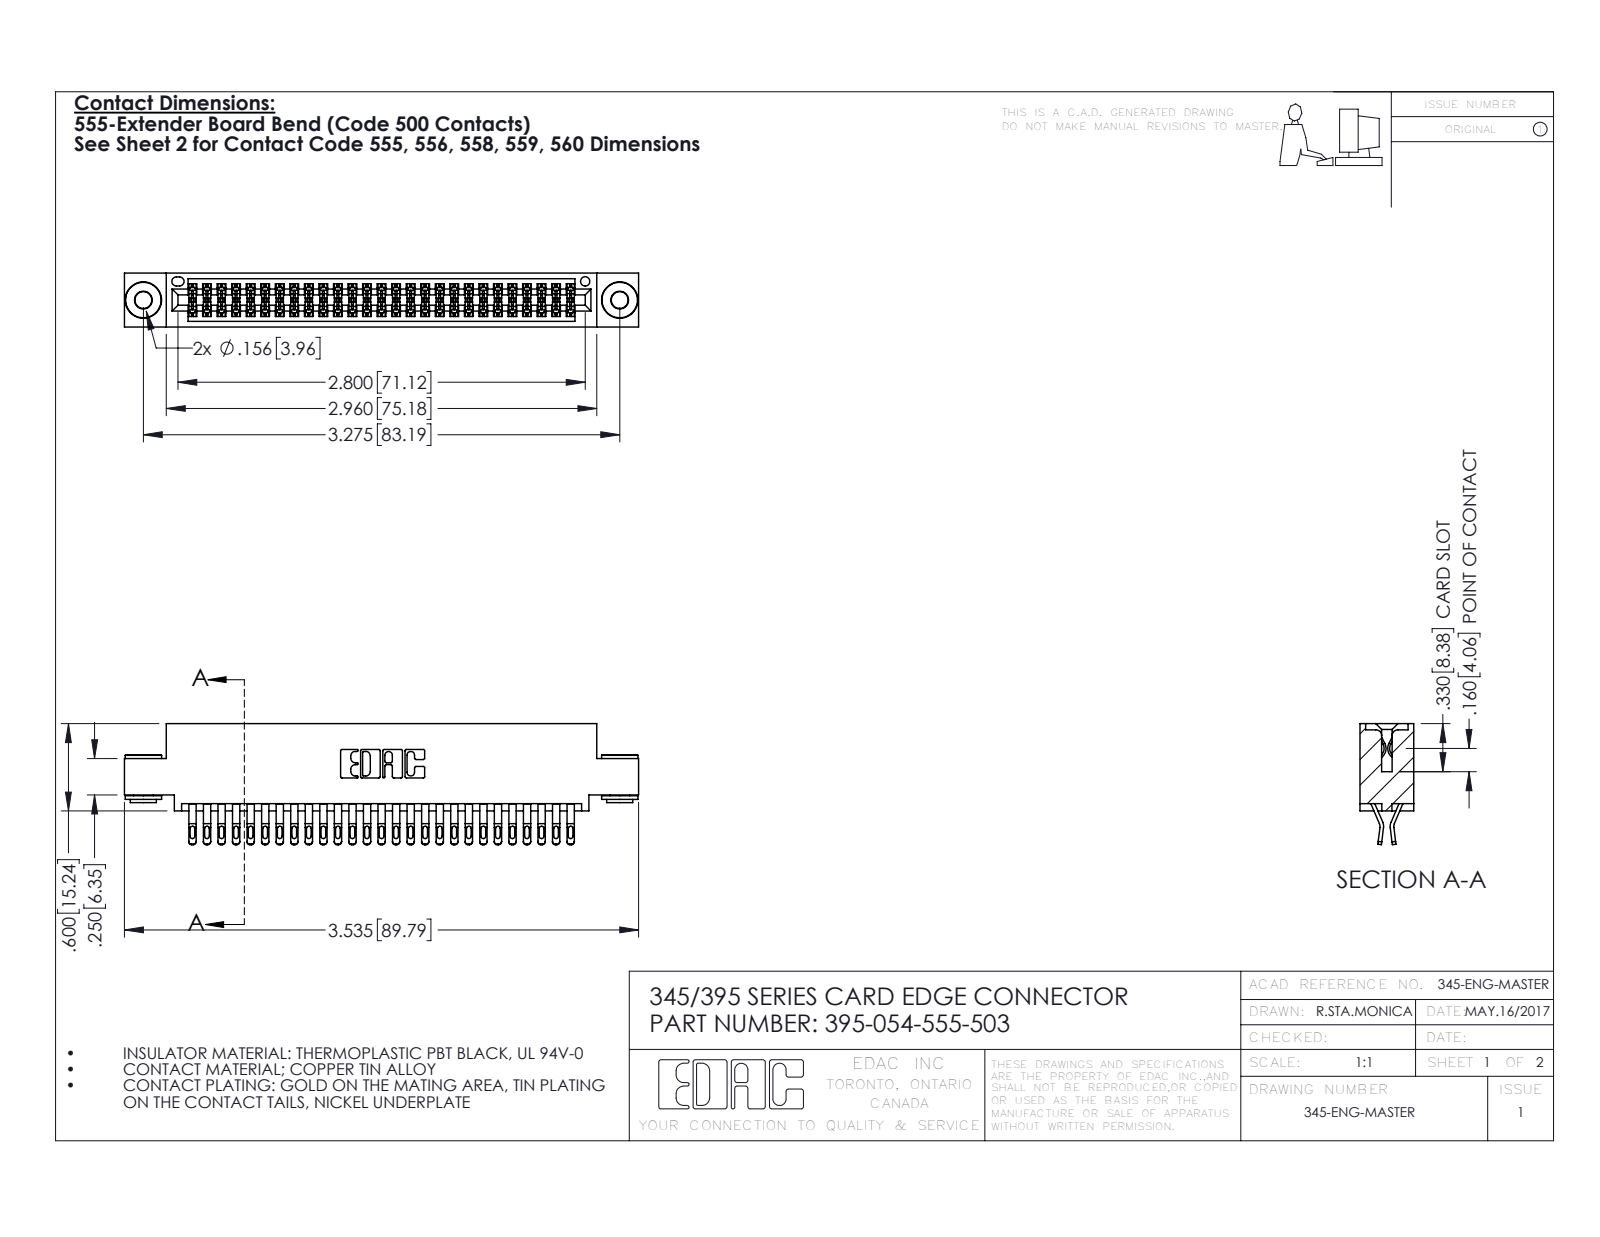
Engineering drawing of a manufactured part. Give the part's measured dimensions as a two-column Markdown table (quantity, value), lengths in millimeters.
| quantity | value |
| --- | --- |
| part name | 395-054-555-503; 345-292-001_555 Tail; 345 Part_0.110 Offset - 0.156 Dia-TH; 345-250-002_345-250-002-102 |
| STEP written by | SolidWorks 2016 (CONFIG_CONTROL_DESIGN) |
| units | millimeters |
| bodies | 57 solids, 3192 faces (1768 planar, 1416 cylindrical, 8 other) |
| overall size | 89.8 × 21.1 × 9.4 |
| volume | 8 690 mm³ |
| surface area | 13 390 mm² |
| round holes (diameter × count) | 2.9 × 2, 4 × 2, 1.6 × 1 |
| round bosses / shafts (diameter × count) | 6.4 × 2, 4.6 × 2, 3.5 × 2 |
| partial cylindrical surfaces (radius × count) | 0.4 × 135, 0.5 × 108, 0.2 × 81, 0.3 × 22, 0.2 × 6, 0.8 × 6, 0.7 × 3, 0.3 × 2 |
| main face-to-face distances | 1.8, 7.6, 0.6, 9.4, 5.1, 2.5, 6.9, 5.7, 4.4, 3.8 |
| hole center spacings | 6.9, 77.2, 83.2 |
